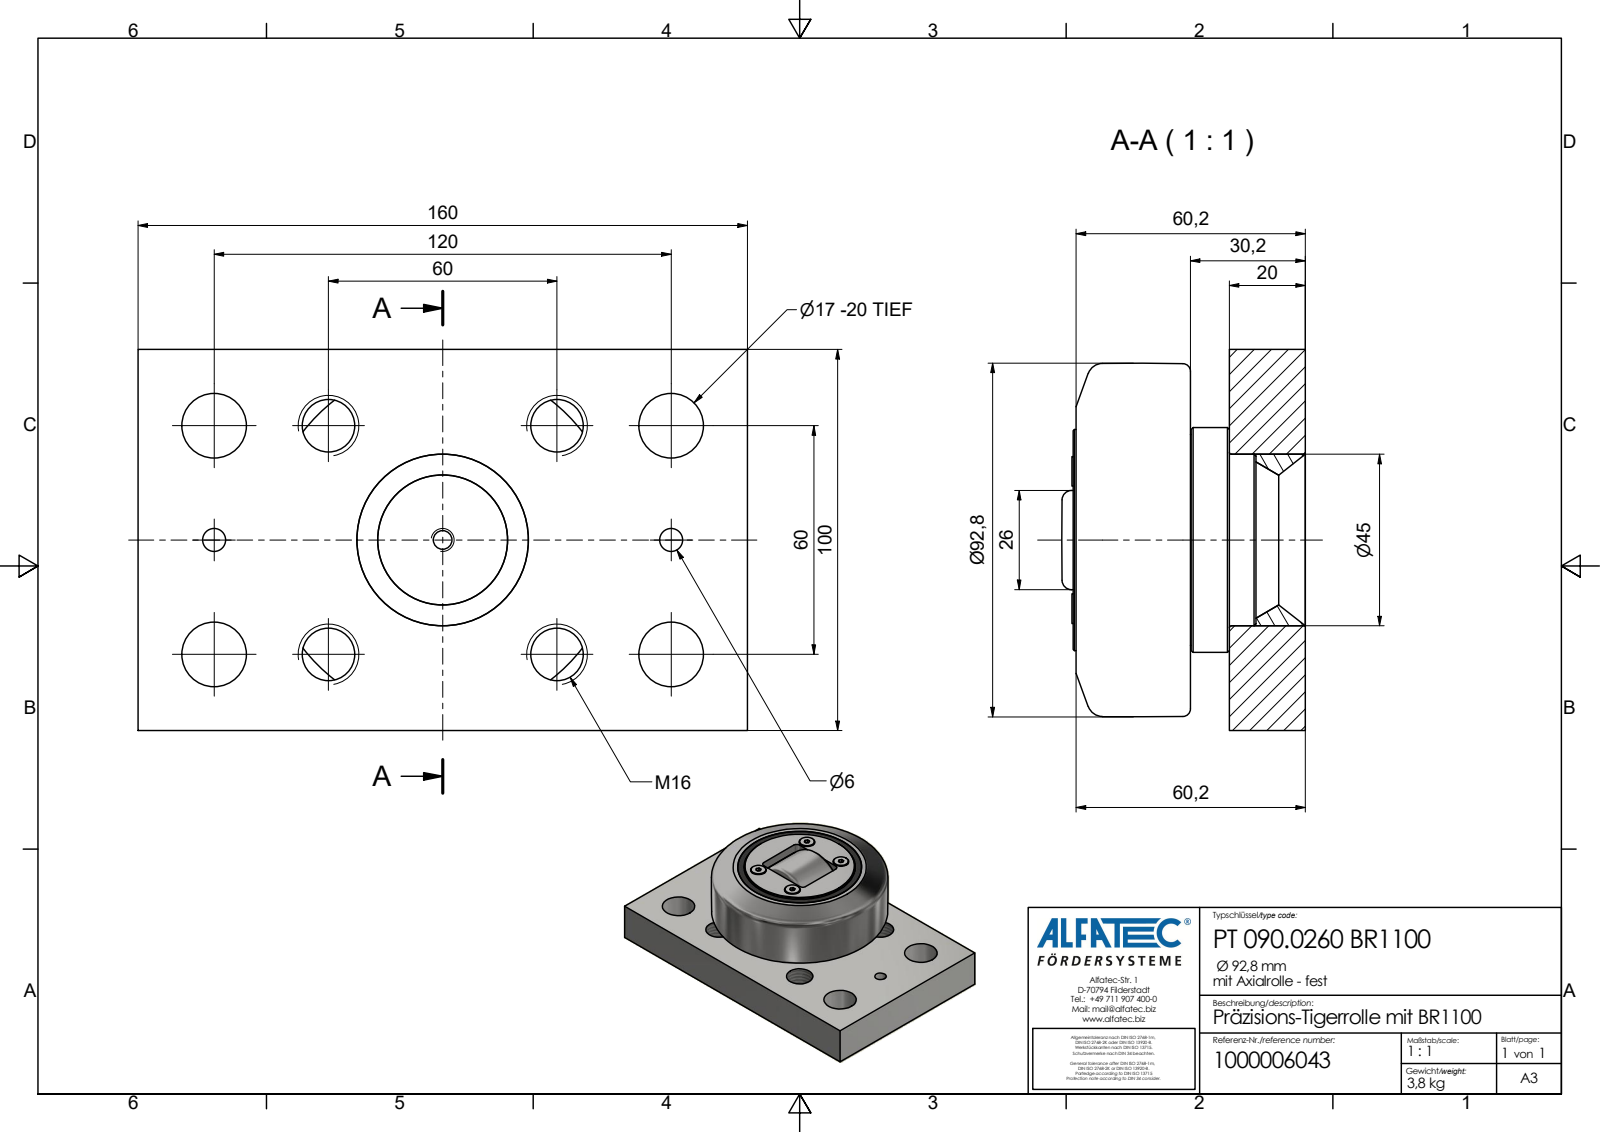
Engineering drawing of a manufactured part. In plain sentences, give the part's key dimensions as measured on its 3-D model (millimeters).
The part is named "PT 090.0260 BR1100_Kontur". Its 3-D file was written by "Autodesk Inventor 2020 (AP242_MANAGED_MODEL_BASED_3D_ENGINEERING_MIM_LF)". It is 1 solid with 92 faces: 52 planar, 25 cylindrical and 15 other. Overall it measures 160 by 100 by 64 millimeters. Its volume is 506 001 cubic millimeters and its surface area 66 883 square millimeters. Round holes: 4 of diameter 13.84, 4 of diameter 17, 2 of diameter 6, 1 of diameter 2.5, 1 of diameter 4.92. Round bosses or shafts: 4 of diameter 7.8, 1 of diameter 59, 1 of diameter 58, 1 of diameter 55.3. Partial cylindrical surfaces (rounded edges, fillets, slot ends): 4 of radius 2, 1 of radius 1.5, 1 of radius 25. The main face-to-face distances are 20, 30.2, 10.2, 100, 160, 30, 61, 41, 30.8, 60.2. The hole center spacings are 30, 42.43, 60, 67.08, 90, 94.87, 108.17, 123.69.
